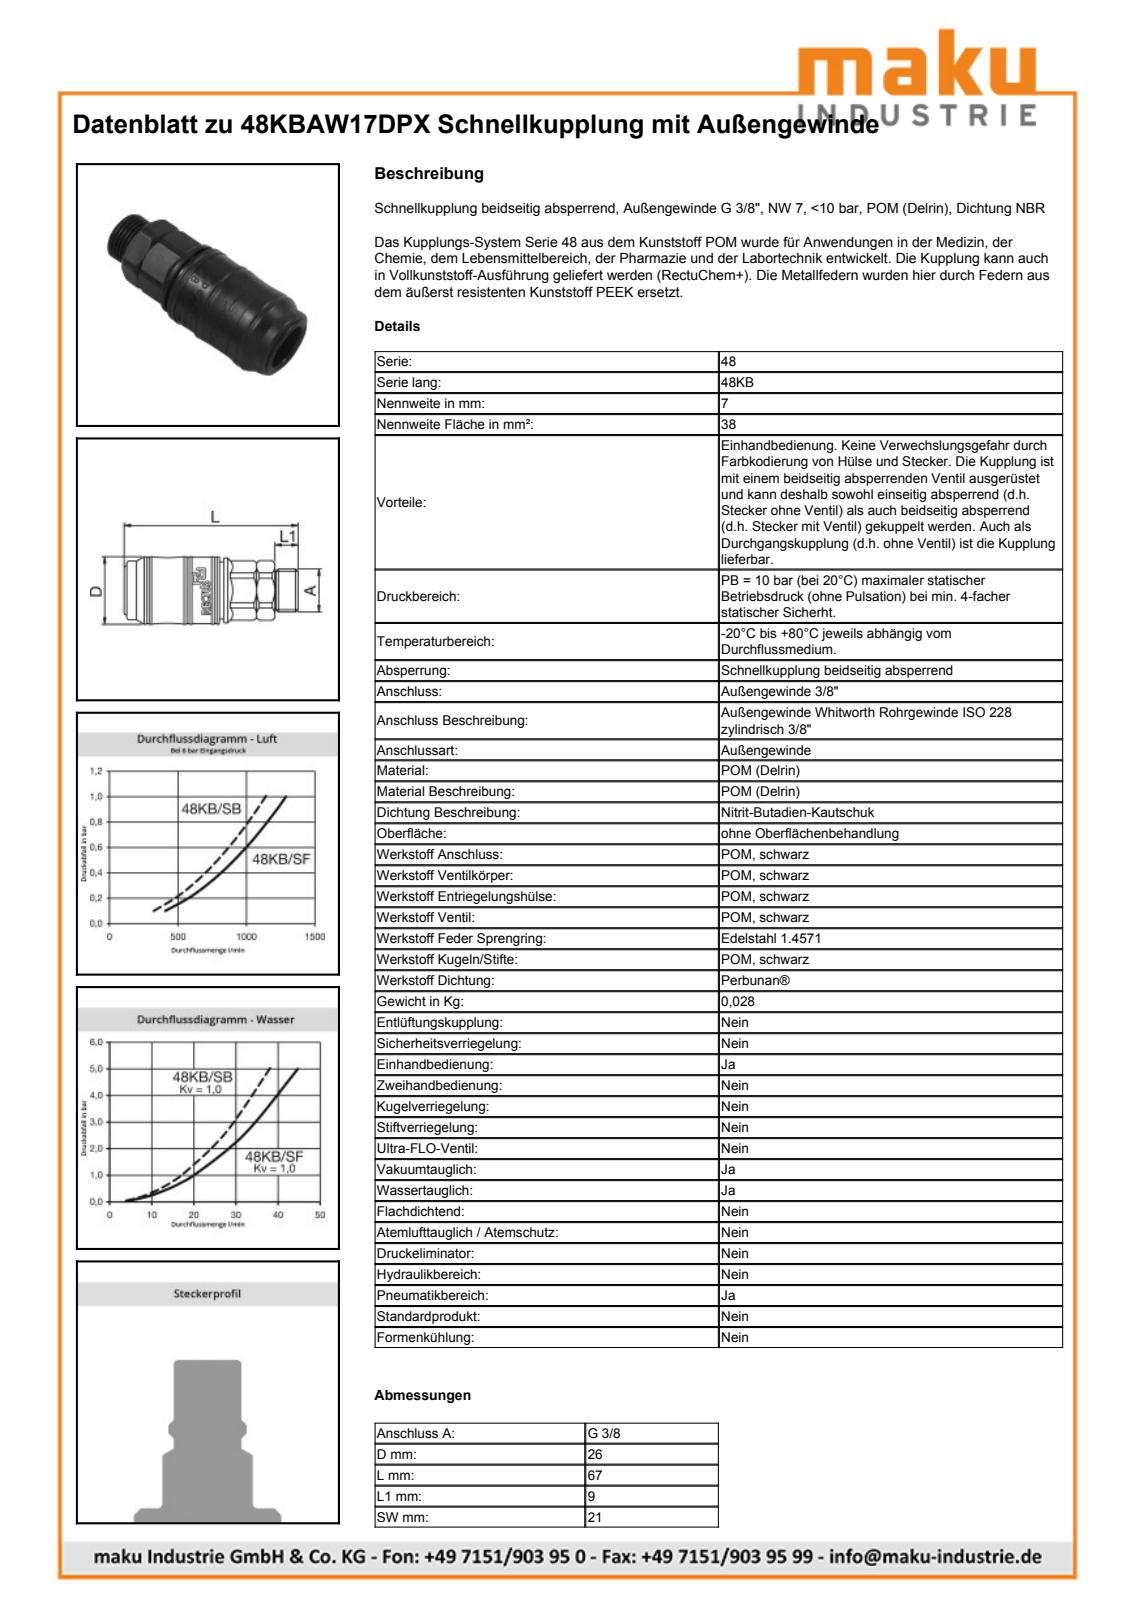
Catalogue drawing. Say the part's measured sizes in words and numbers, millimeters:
The part is named "D110585". Its 3-D file was written by "Autodesk Inventor 2013 (AUTOMOTIVE_DESIGN)". It is 1 solid with 642 faces: 265 planar, 87 cylindrical and 290 other. Overall it measures 67 by 26 by 26 millimeters. Its volume is 24 918 cubic millimeters and its surface area 11 467 square millimeters. Round holes: 1 of diameter 18, 1 of diameter 18.7, 1 of diameter 22.7. Round bosses or shafts: 1 of diameter 26, 1 of diameter 25.4, 1 of diameter 25, 1 of diameter 22.6, 1 of diameter 22.4, 1 of diameter 19, 1 of diameter 18.4, 1 of diameter 16.66. Partial cylindrical surfaces (rounded edges, fillets, slot ends): 1 of radius 10, 1 of radius 11.5, 1 of radius 12.8, 1 of radius 12.9. The main face-to-face distances are 21, 67, 9, 58, 5.62, 31.2, 22.2, 35.8, 2.5, 66.
